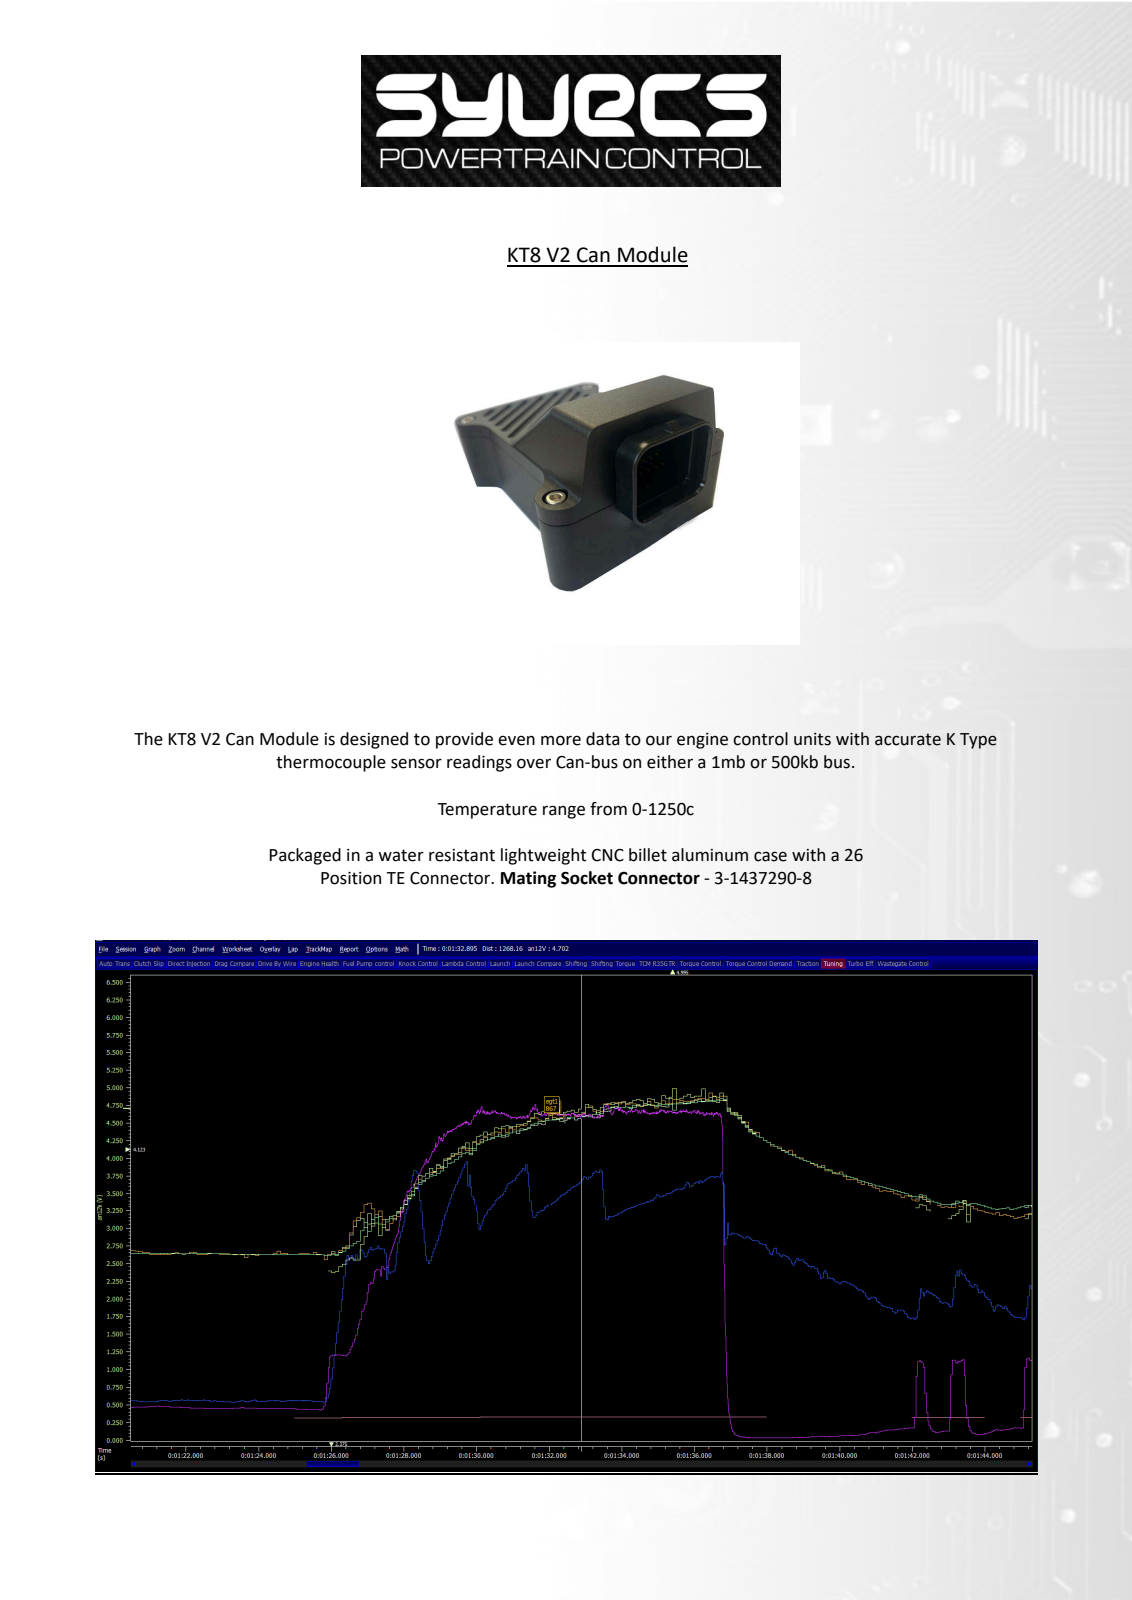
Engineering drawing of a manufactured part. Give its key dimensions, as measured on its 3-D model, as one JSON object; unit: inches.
{"part_name": "TCB2HBD-2; CAP_PANASONIC_E7; KT8_v2; TCB2HBD - CASE_BOT_Rev001 (+8 more)", "step_written_by": "SolidWorks 2020 (CONFIG_CONTROL_DESIGN)", "units": "inches", "bodies": {"solids": 14, "faces": 3799, "planar": 2333, "cylindrical": 1102, "other": 364}, "overall_size": [3.508, 2.683, 1.858], "volume_in3": 4.623, "surface_area_in2": 97.92, "round_holes": [[0.039, 110], [0.043, 58], [0.031, 40], [0.051, 26], [0.057, 8], [0.098, 8], [0.126, 6], [0.134, 4], [0.256, 4], [0.44, 1]], "round_bosses_or_shafts": [[0.039, 16], [0.315, 4], [0.256, 4], [0.244, 4], [0.102, 2]], "partial_cylinders_radius": [[0.004, 31], [0.02, 24], [0.008, 13], [0.059, 12], [0.01, 11], [0.118, 7], [0.039, 6], [0.197, 5]], "face_to_face_distances": [0.098, 0.946, 0.177, 0.769, 0.305, 0.276, 0.464, 0.641, 0.161, 0.24], "hole_center_spacings": [0.118, 0.15, 0.236, 0.301, 0.224, 0.344, 0.354, 0.1]}
